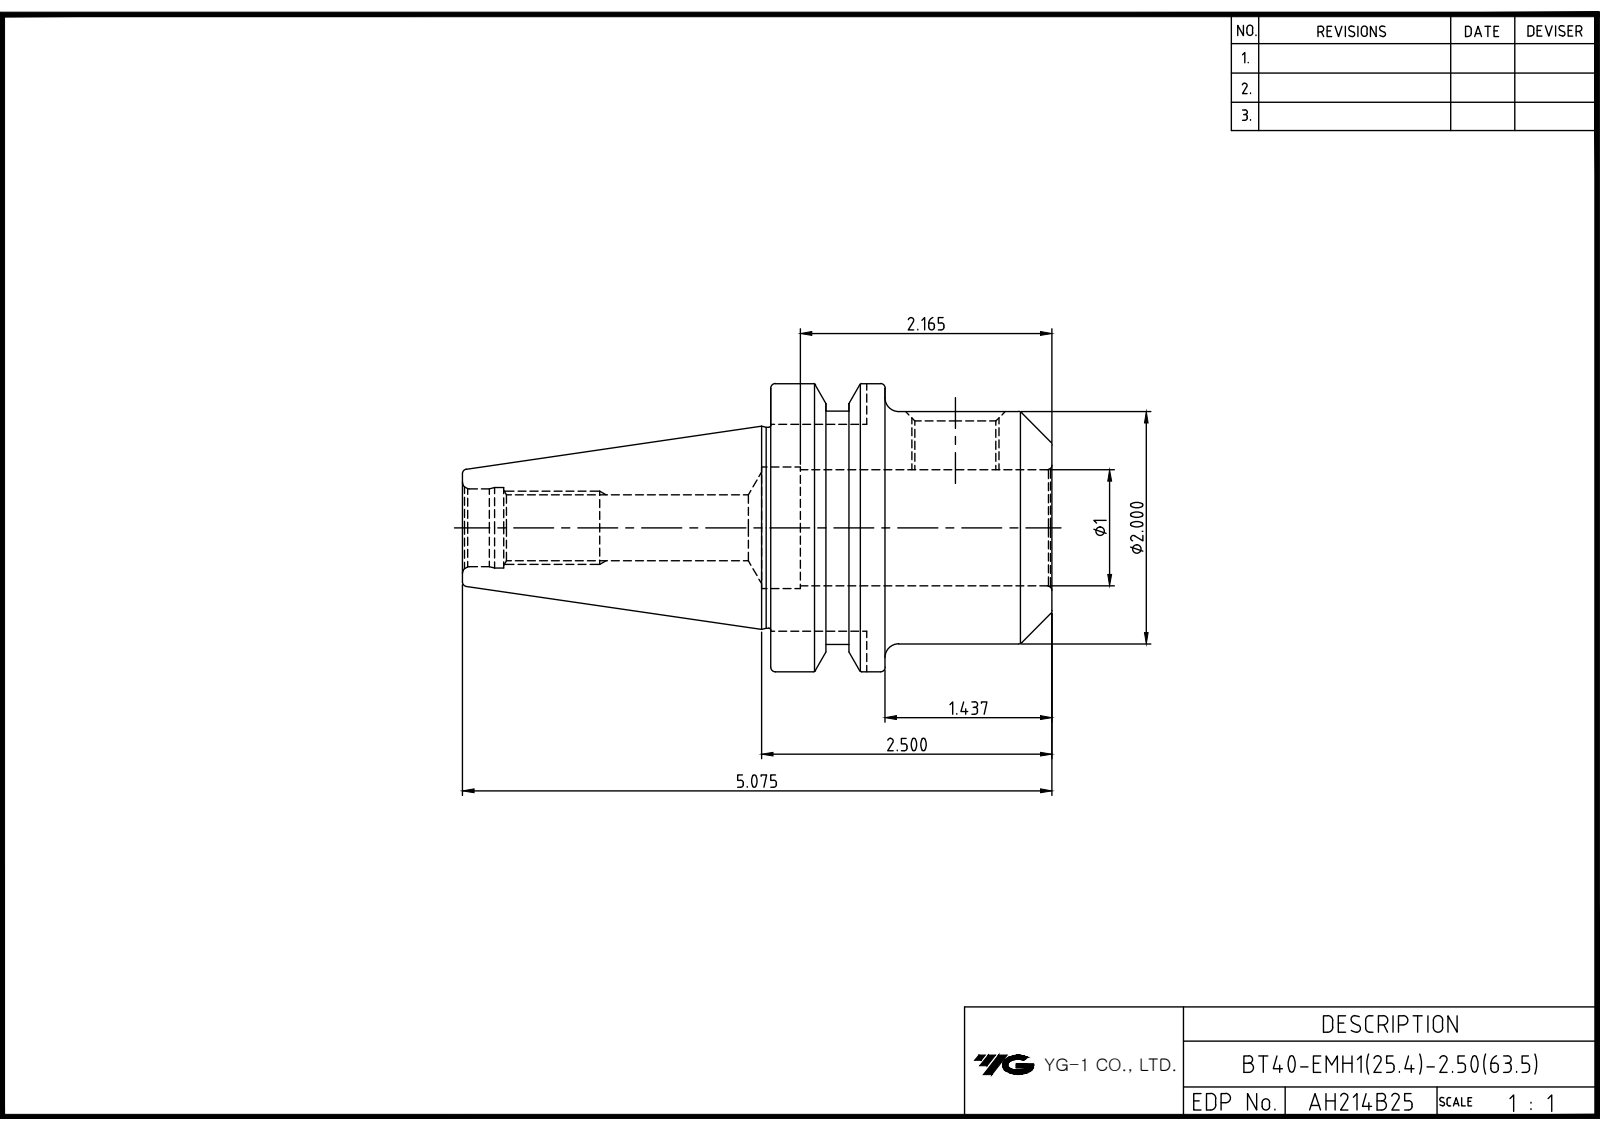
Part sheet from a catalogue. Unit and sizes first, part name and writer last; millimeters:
Units: millimetres
Overall size (bounding box): 128.9 × 63 × 63
Round holes (diameter × count): ⌀13.5 ×1, ⌀13.84 ×1, ⌀17 ×1, ⌀17.32 ×1, ⌀17.6 ×1, ⌀25.4 ×1, ⌀26.6 ×1
Round bosses / shafts (diameter × count): ⌀63 ×1, ⌀52.6 ×1, ⌀50.8 ×1, ⌀44 ×1
Partial cylindrical surfaces — rounded edges, fillets, slot ends (radius × count): R8.05 ×1
Main face-to-face distances: 61.5, 25, 36.5, 45.2, 16.1, 67.4, 92.4, 128.9, 84.5, 17.1
Volume: 158 315 mm³ · Surface area: 31 509 mm²
Bodies: 1 solid, 54 faces (18 planar, 16 cylindrical, 20 other)
Part name (STEP PRODUCT): LO-BT40-EMH25.4-63.5
STEP written by: Autodesk Inventor 2022 (AUTOMOTIVE_DESIGN)
